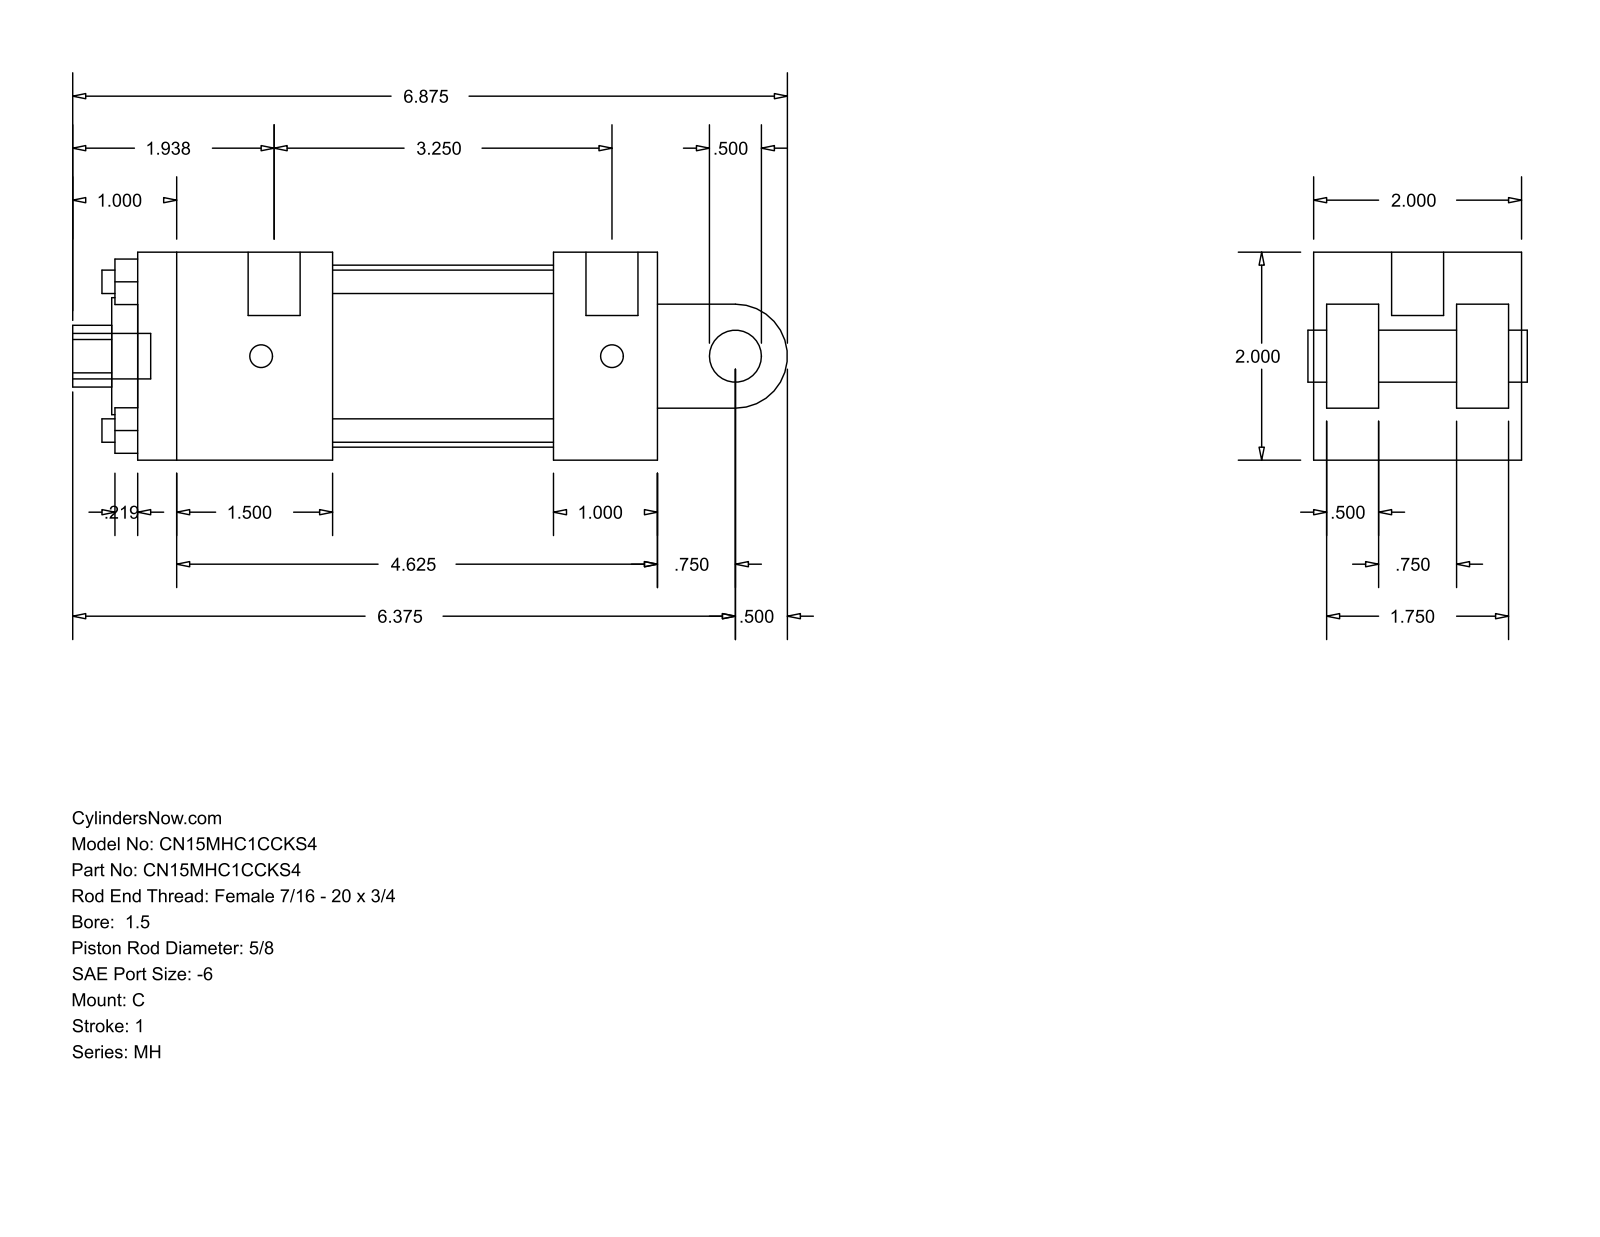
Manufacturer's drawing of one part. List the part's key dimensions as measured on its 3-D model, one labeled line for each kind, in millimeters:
Part name (STEP PRODUCT): MH_C__0150_0.625
STEP written by: GSSL Pune (CONFIG_CONTROL_DESIGN)
Units: millimetres
Bodies: 0 solids, 99 faces (70 planar, 29 cylindrical, 0 other)
Overall size (bounding box): 174.62 × 50.8 × 50.8
Round holes (diameter × count): ⌀5.71 ×4, ⌀5.56 ×2, ⌀12.7 ×1, ⌀15.88 ×1, ⌀28.57 ×1, ⌀44.45 ×1
Round bosses / shafts (diameter × count): ⌀12.7 ×2, ⌀5.56 ×2, ⌀11.11 ×1
Partial cylindrical surfaces — rounded edges, fillets, slot ends (radius × count): R7.54 ×1, R12.7 ×1
Main face-to-face distances: 50.8, 12.7, 127, 53.97, 3.17, 47.63, 15.87, 34.93, 31.76, 38.1
Hole centre spacings: 25.68, 36.32, 51.36
